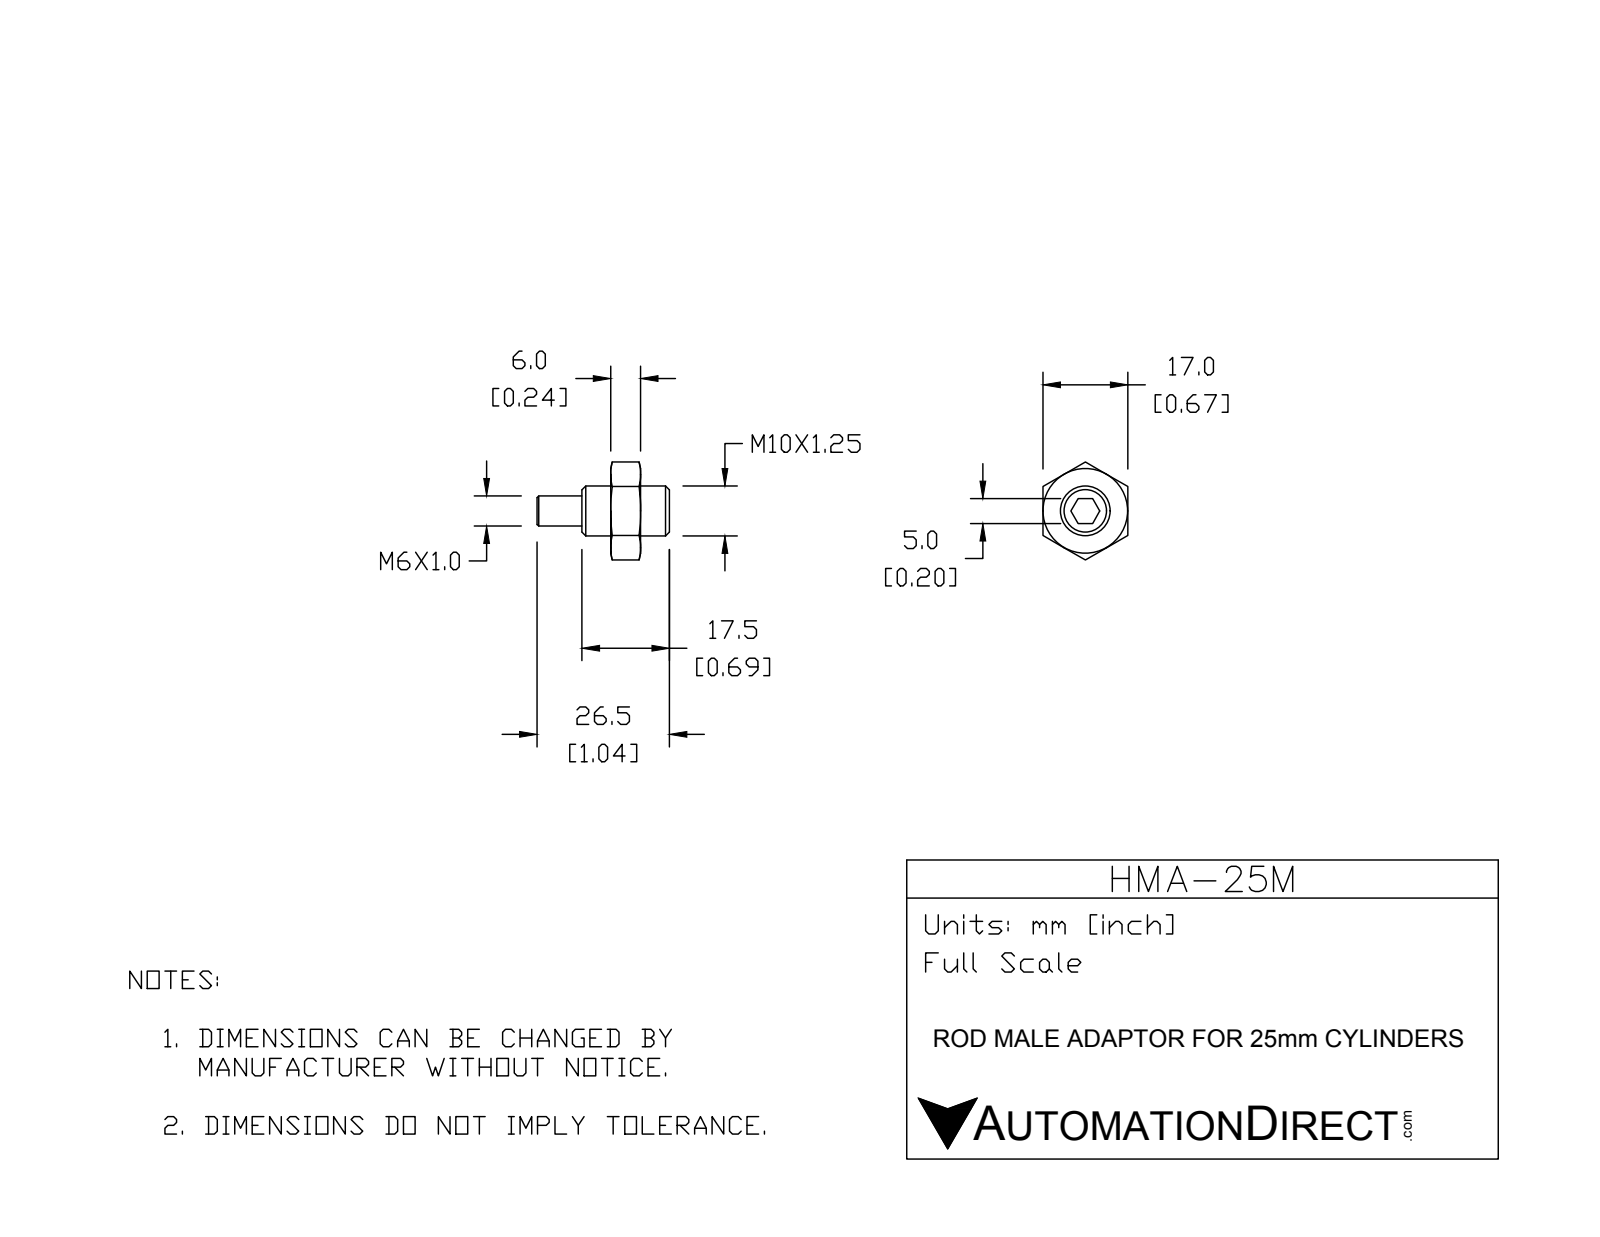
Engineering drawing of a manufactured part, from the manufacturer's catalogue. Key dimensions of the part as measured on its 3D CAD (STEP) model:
Part name (STEP PRODUCT): HMA-25M
STEP written by: SolidWorks 2015 (CONFIG_CONTROL_DESIGN)
Units: millimetres
Bodies: 2 solids, 44 faces (18 planar, 6 cylindrical, 20 other)
Overall size (bounding box): 26.5 × 19.63 × 17
Volume: 2 539 mm³ · Surface area: 1 795 mm²
Round holes (diameter × count): ⌀10 ×1
Round bosses / shafts (diameter × count): ⌀6 ×1
Main face-to-face distances: 17, 6, 5.75, 11.75, 5, 17.5, 26.5, 20.75, 14.75, 9
